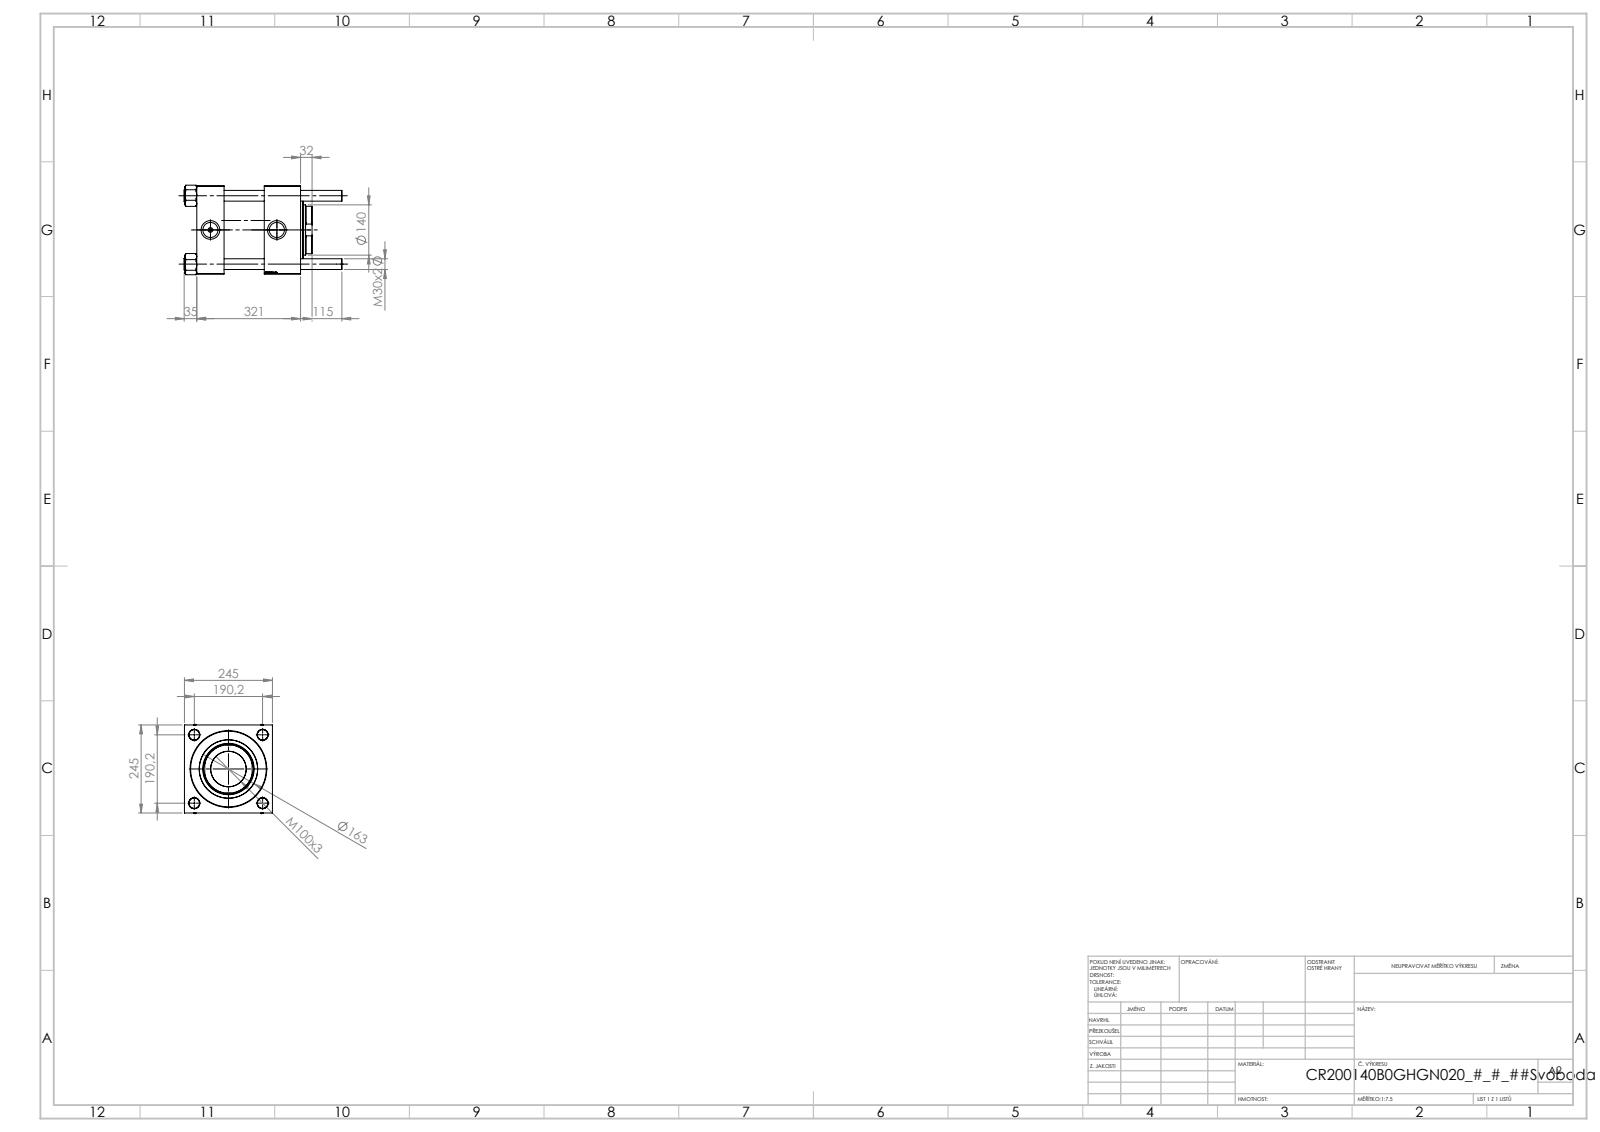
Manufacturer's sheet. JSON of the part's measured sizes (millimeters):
{"part_name": "NUT_M5_B; V215_VC_A; V215CR_VCP_B; V215CR_B-1 (+1 more)", "step_written_by": "SolidWorks 2019 (CONFIG_CONTROL_DESIGN)", "units": "millimeters", "bodies": {"solids": 11, "faces": 1206, "planar": 480, "cylindrical": 78, "other": 648}, "overall_size": [439, 249.22, 245], "volume_mm3": 14390000, "surface_area_mm2": 1154000, "round_holes": [[30, 4], [7, 2], [41.92, 2], [52, 2], [98.5, 1], [140, 1], [143, 1], [146, 1], [200, 1], [210.5, 1]], "round_bosses_or_shafts": [[33, 4], [206, 1], [163, 1]], "partial_cylinders_radius": [[68, 1]], "face_to_face_distances": [245, 76, 188, 112, 260.3, 184.3, 72.3, 101, 289, 213], "hole_center_spacings": [134.49, 190.2, 268.98, 185]}
